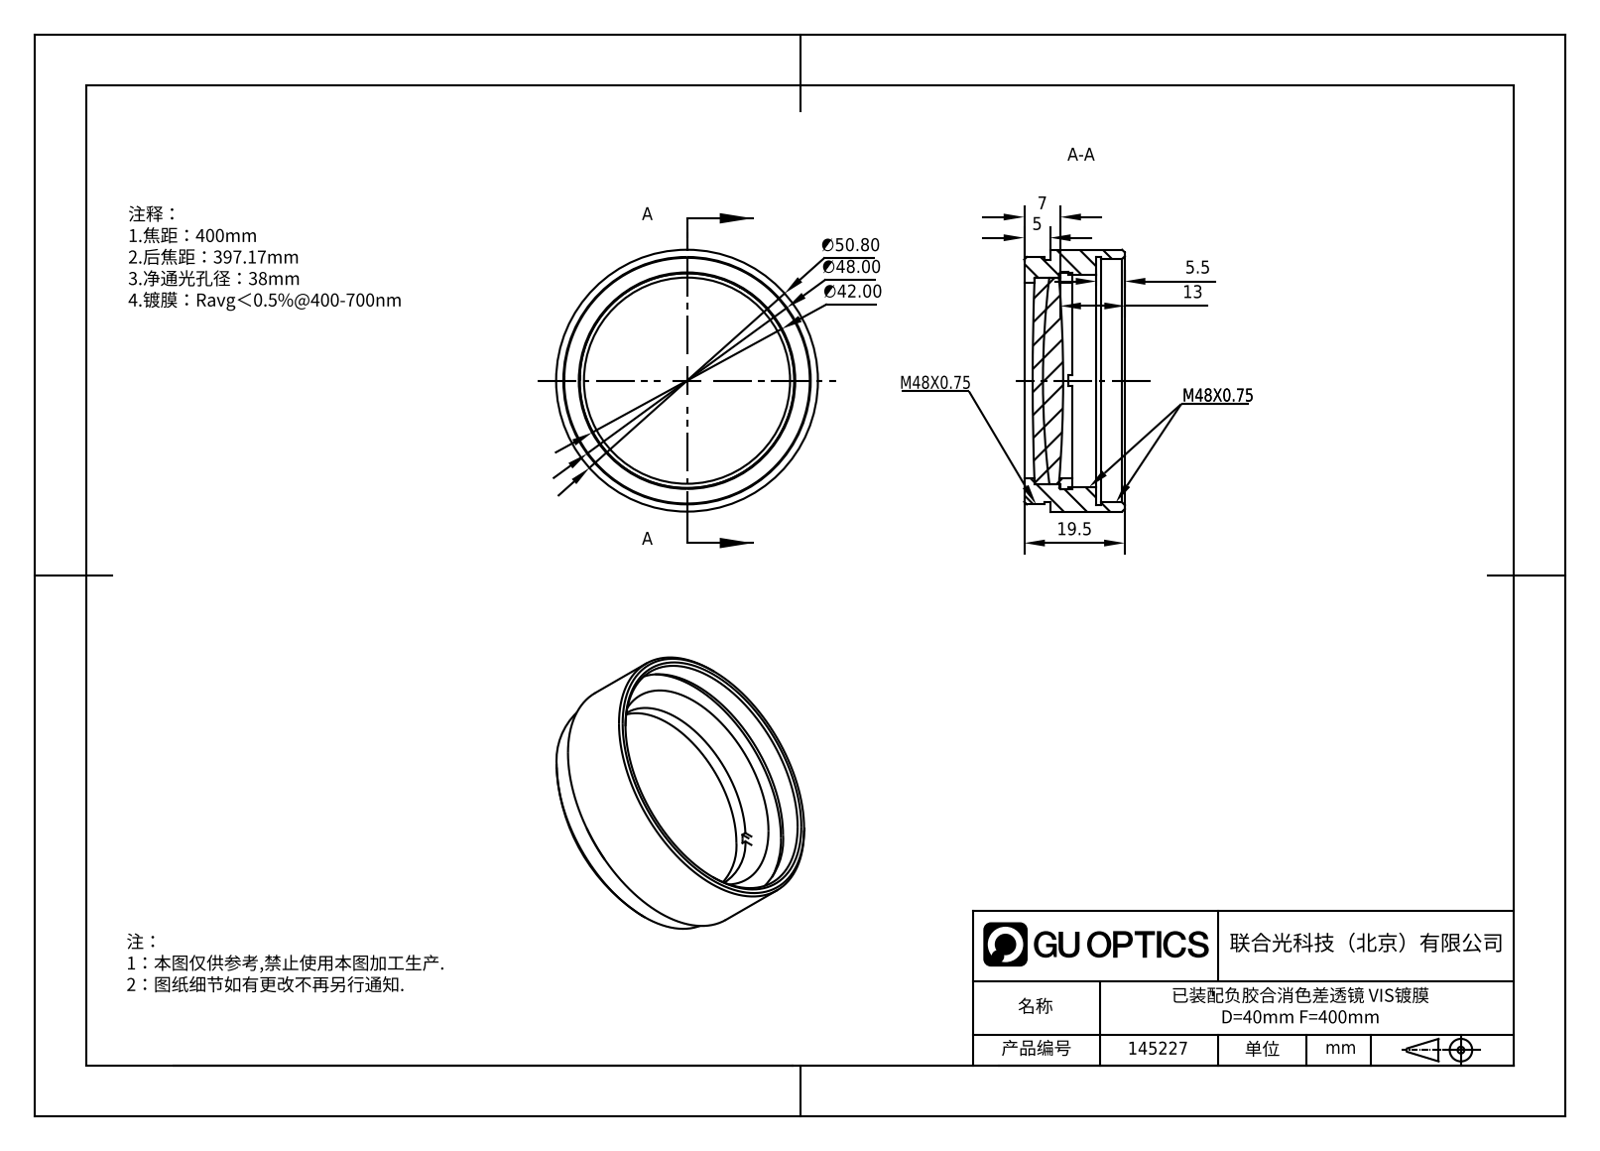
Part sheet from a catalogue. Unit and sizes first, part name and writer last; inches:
Units: inches
Overall size (bounding box): 2 × 2 × 0.768
Round holes (diameter × count): ⌀1.496 ×1, ⌀1.624 ×1, ⌀1.657 ×1, ⌀1.86 ×1, ⌀1.894 ×1
Round bosses / shafts (diameter × count): ⌀2 ×1, ⌀1.89 ×1, ⌀1.85 ×1, ⌀1.654 ×1, ⌀1.575 ×1
Main face-to-face distances: 0.551, 0.197, 0.079, 0.354, 0.276, 0.367, 0.17, 0.184, 0.269, 0.072
Volume: 1.093 in³ · Surface area: 22.36 in²
Bodies: 4 solids, 64 faces (18 planar, 26 cylindrical, 20 other)
Part name (STEP PRODUCT): GL31-040-400-VIS_Solidworks; APD-ML40-400-VIS-A; M42x0.75ѹȦ; M42x0.75安装环PN35008-LM400-D1
STEP written by: SolidWorks 2022 (AUTOMOTIVE_DESIGN)
